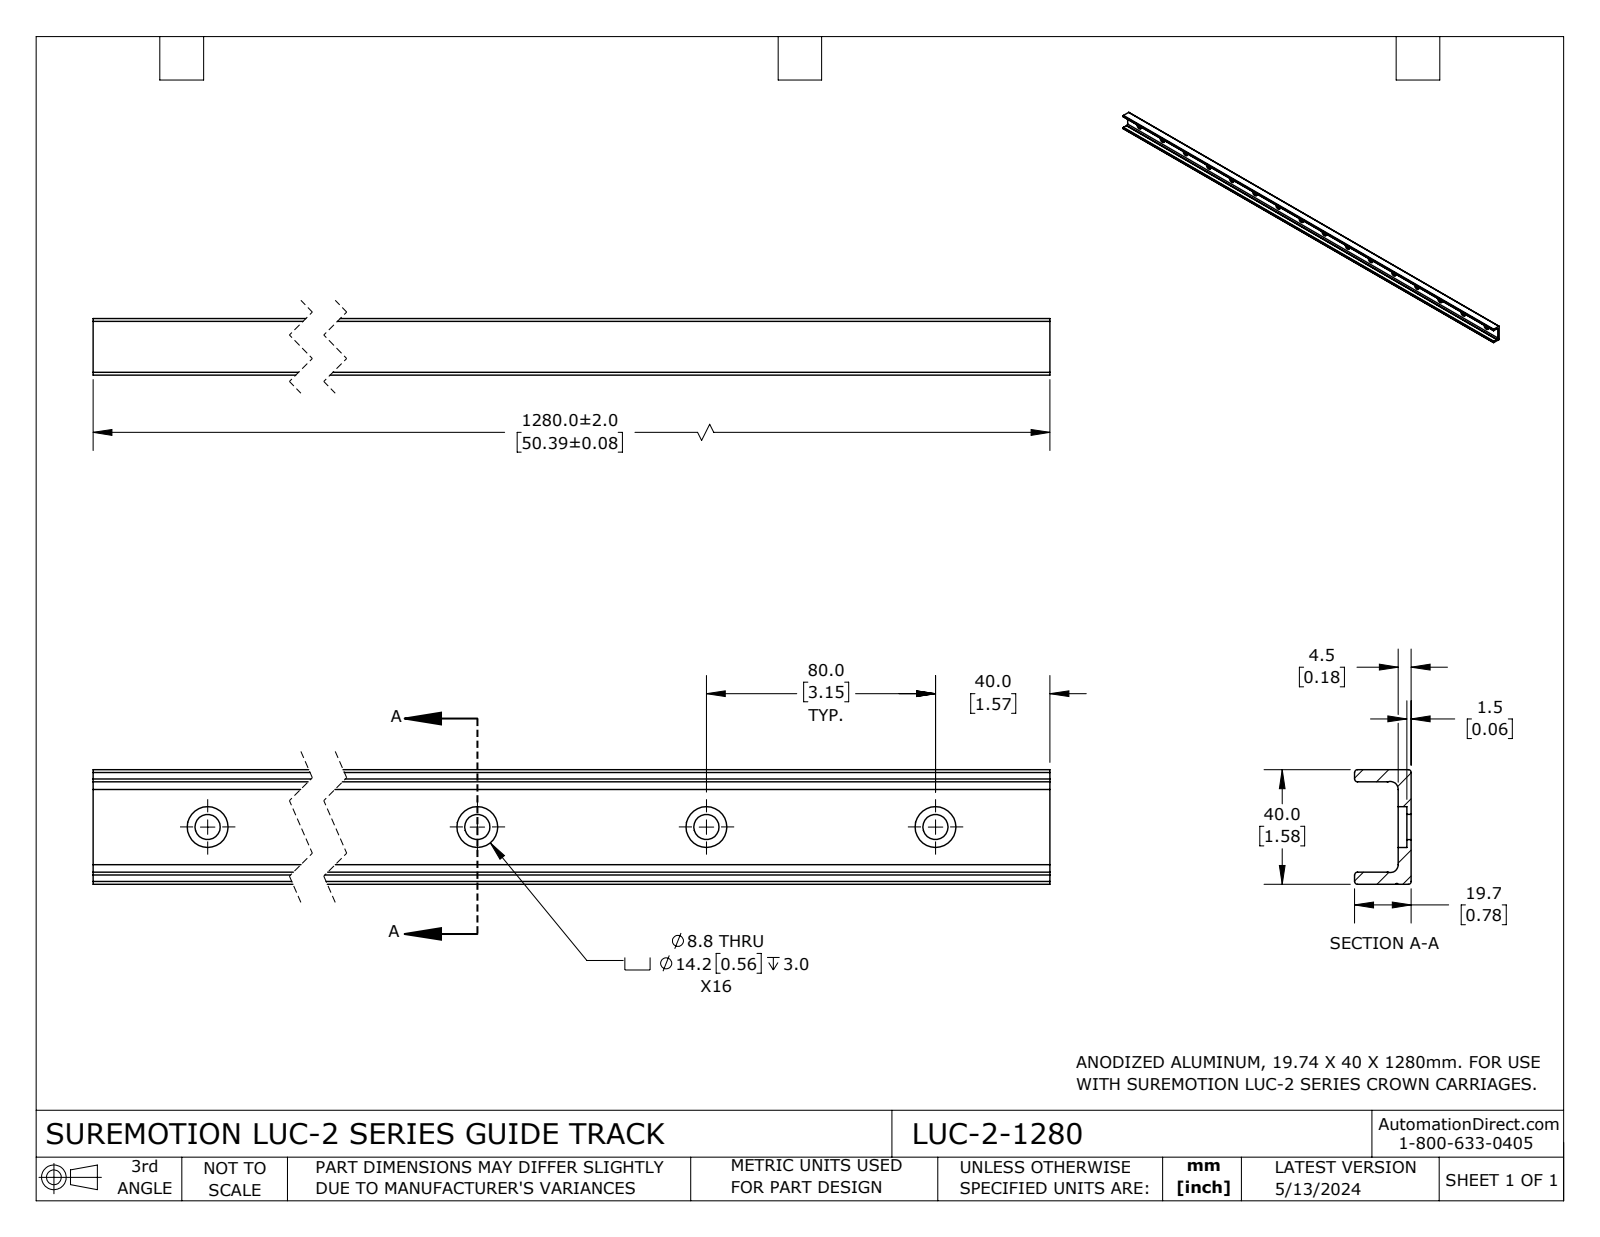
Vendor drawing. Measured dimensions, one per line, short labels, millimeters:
name: LUC-2-1280
written by: SolidWorks 2023 (CONFIG_CONTROL_DESIGN)
unit: mm
bodies: 1 solid, 102 faces (27 planar, 75 cylindrical, 0 other)
size: 1280 × 40.01 × 19.74
volume: 388 426 mm³; area: 188 050 mm²
holes: 16× ⌀8.81, 16× ⌀14.25
rounds: 8× R0.99, 2× R2.77, 1× R0.33
face distances: 4.5, 4.26, 35.76, 40.02, 31.5, 19.74, 15.24, 1.5, 3, 18.24
hole spacings: 80, 160, 240, 320, 400, 480, 560, 640
